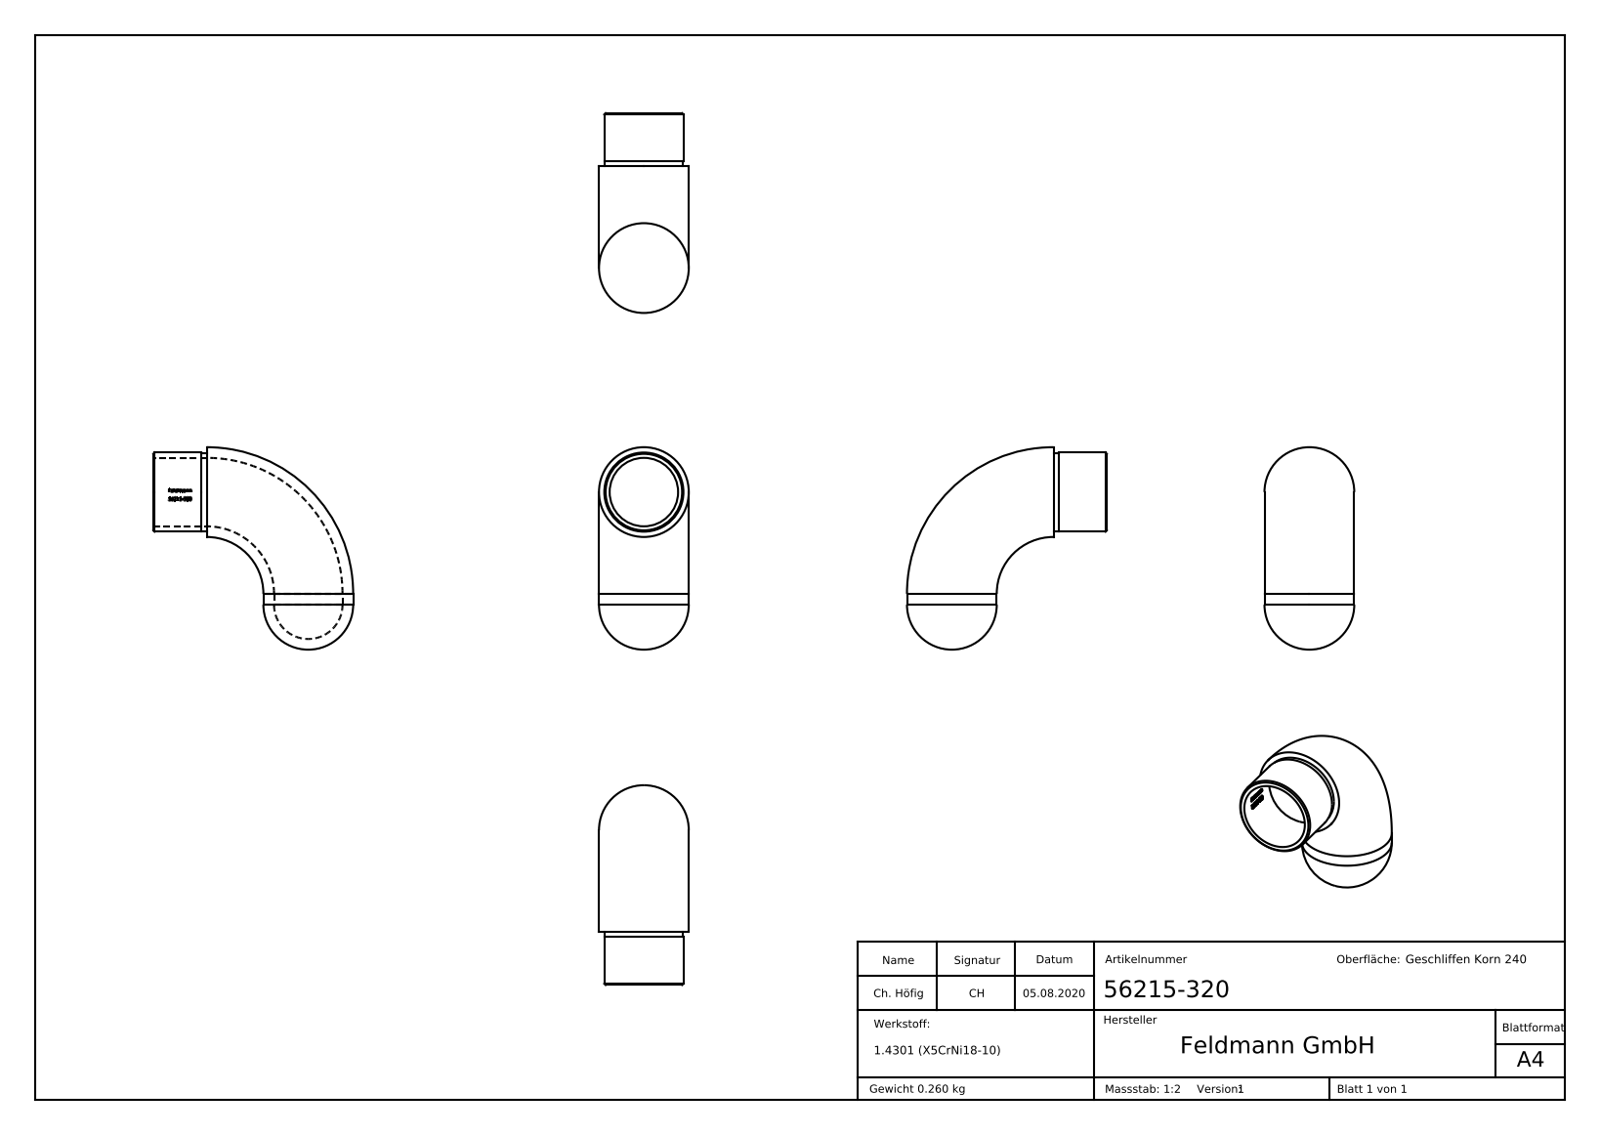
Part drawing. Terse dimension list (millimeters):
name: 56215-320
written by: SolidWorks 2018 (CONFIG_CONTROL_DESIGN)
unit: mm
bodies: 1 solid, 256 faces (97 planar, 41 cylindrical, 118 other)
size: 76 × 75 × 33.7
volume: 32 913 mm³; area: 18 658 mm²
holes: 2× ⌀25.7
bosses: 1× ⌀33.7, 1× ⌀29.7, 1× ⌀29.2
rounds: 1× R12.95
face distances: 20, 2, 18, 2.97, 1.32, 3.53, 1.4, 0.39, 2.02, 3.66
